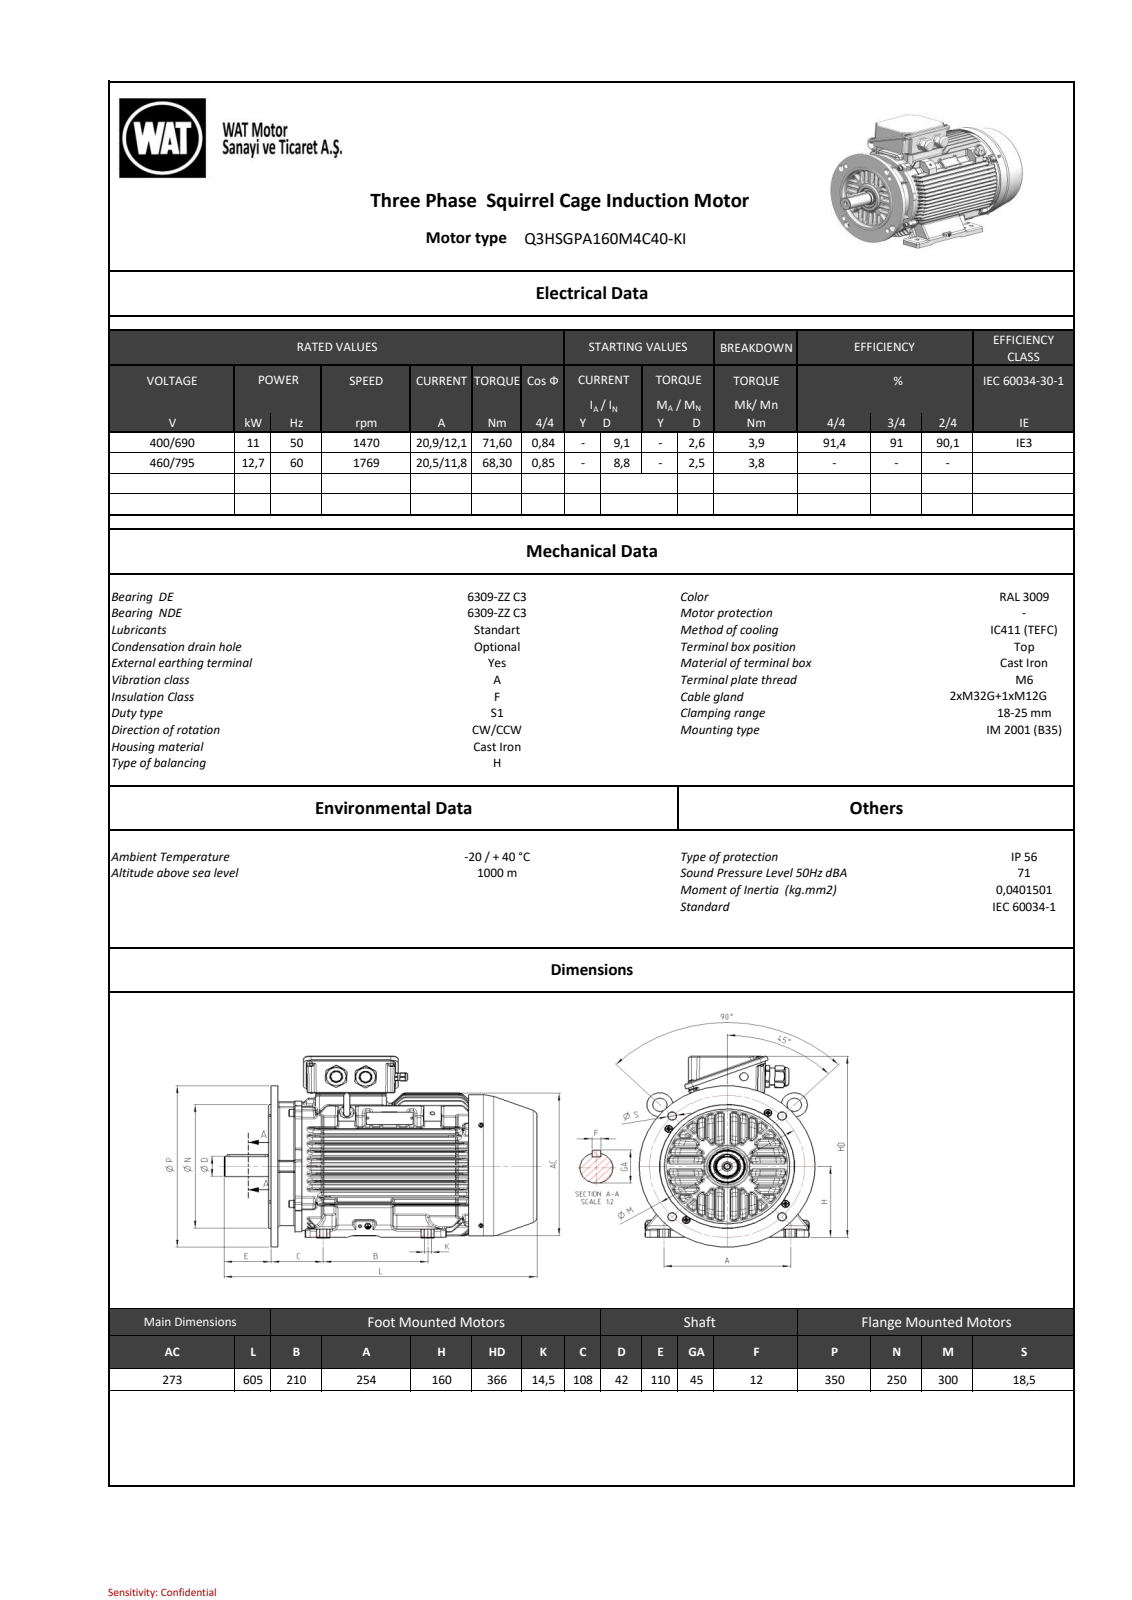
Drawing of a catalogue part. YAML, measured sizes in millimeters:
part_name: "26000C948E142slb"
step_written_by: "SIEMENS PLM Software NX 11.0 (AUTOMOTIVE_DESIGN)"
units: millimeters
bodies: {solids: 0, faces: 6785, planar: 1218, cylindrical: 1829, other: 3738}
overall_size: [605, 380.49, 349]
round_holes:
  - {diameter: 6.8, count: 8}
  - {diameter: 15, count: 4}
  - {diameter: 2.5, count: 2}
  - {diameter: 3.2, count: 2}
  - {diameter: 8.5, count: 2}
  - {diameter: 4.2, count: 1}
  - {diameter: 13, count: 1}
  - {diameter: 19, count: 1}
  - {diameter: 21, count: 1}
  - {diameter: 68.67, count: 1}
  - {diameter: 180, count: 1}
  - {diameter: 264, count: 1}
round_bosses_or_shafts:
  - {diameter: 10, count: 4}
  - {diameter: 8.65, count: 4}
  - {diameter: 8, count: 4}
  - {diameter: 5, count: 4}
  - {diameter: 25, count: 2}
  - {diameter: 349, count: 1}
  - {diameter: 267, count: 1}
  - {diameter: 251, count: 1}
partial_cylinders:
  - {radius: 3, count: 228}
  - {radius: 4.5, count: 212}
  - {radius: 1.5, count: 106}
  - {radius: 4, count: 99}
  - {radius: 2, count: 63}
  - {radius: 1.8, count: 60}
  - {radius: 6, count: 59}
  - {radius: 35, count: 24}
face_to_face_distances: [13.76, 13.83, 27.59, 27.73, 13.9, 41.49, 55.44, 41.68, 27.85, 13.95]
hole_center_spacings: [121.5, 171.83, 42.2, 139.38, 199.06, 239.31, 243.01, 35.5]
